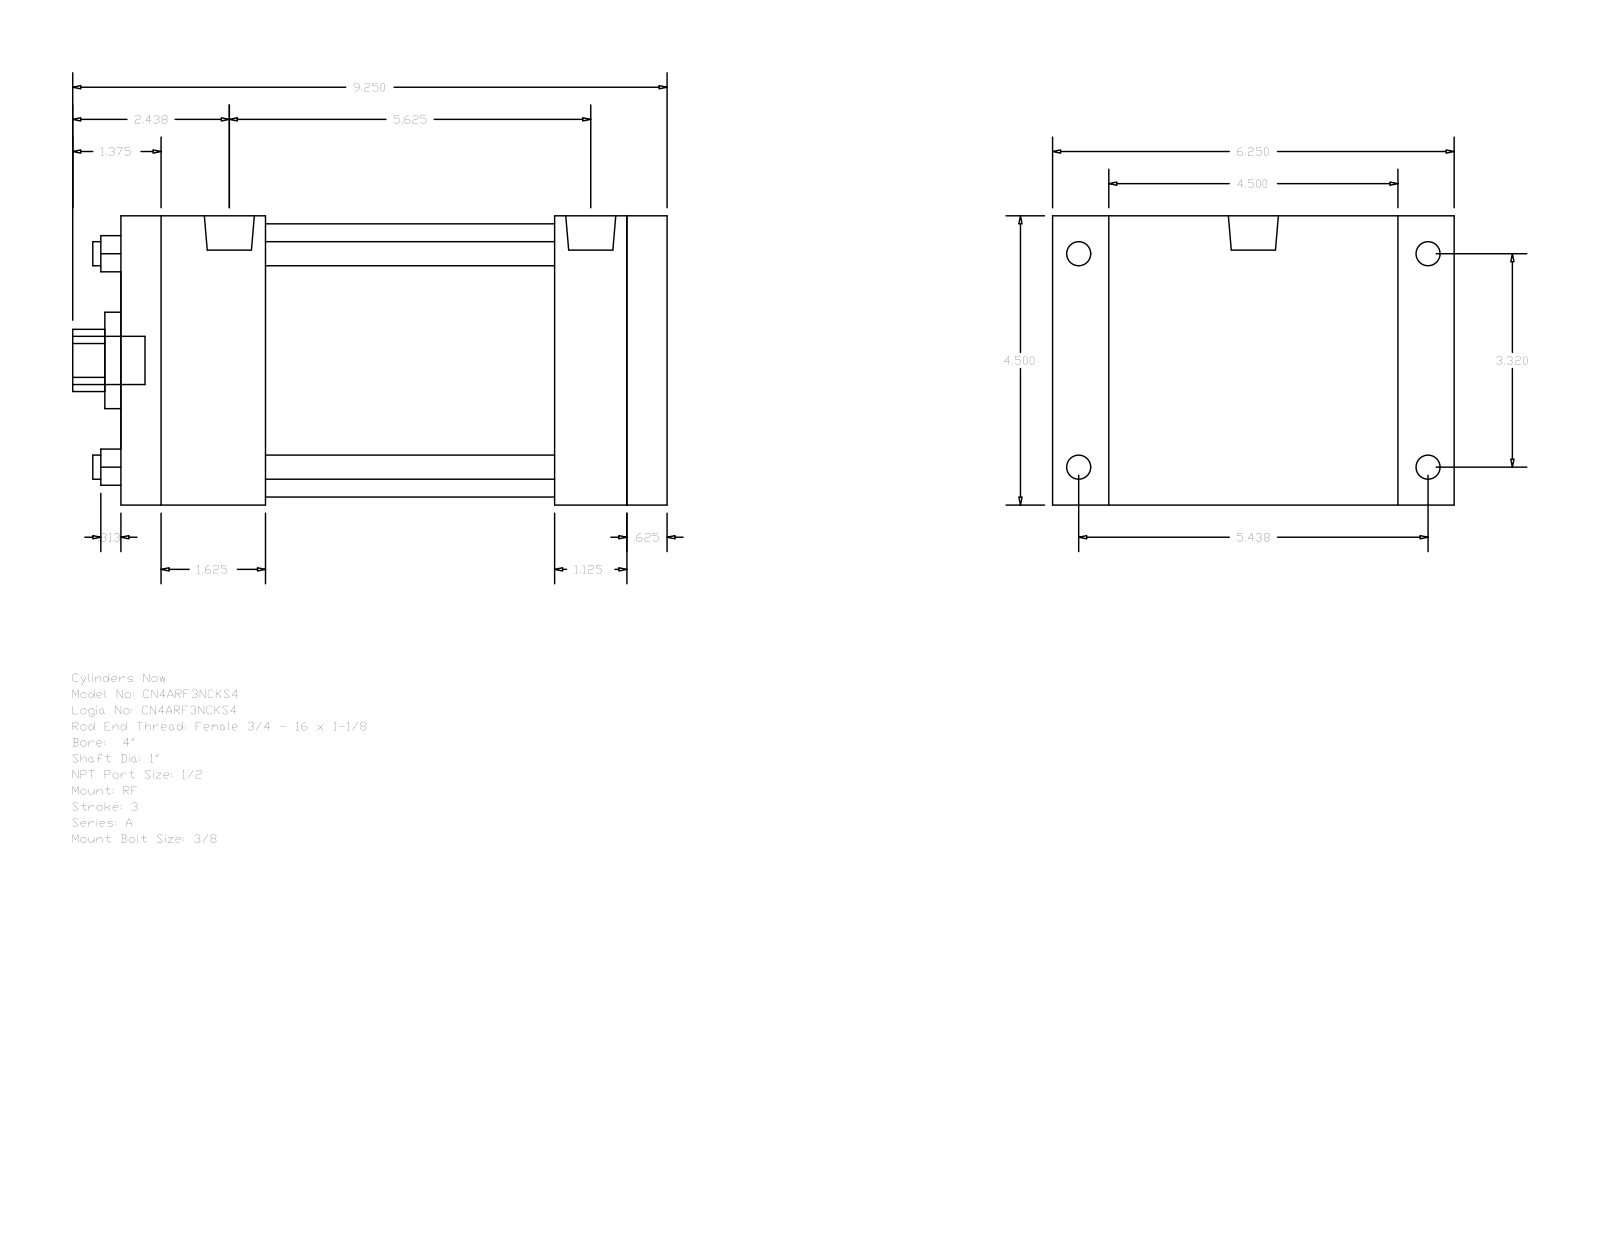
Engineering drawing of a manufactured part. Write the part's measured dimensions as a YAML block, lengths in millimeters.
part_name: "A_RF__0400_1"
step_written_by: "GSSL Pune (CONFIG_CONTROL_DESIGN)"
units: millimeters
bodies: {solids: 0, faces: 92, planar: 64, cylindrical: 28, other: 0}
overall_size: [234.95, 158.75, 114.3]
round_holes:
  - {diameter: 9.53, count: 4}
  - {diameter: 25.4, count: 1}
  - {diameter: 38.1, count: 1}
  - {diameter: 107.95, count: 1}
round_bosses_or_shafts:
  - {diameter: 9.53, count: 4}
  - {diameter: 8.73, count: 4}
  - {diameter: 19.77, count: 2}
  - {diameter: 19.05, count: 1}
partial_cylinders:
  - {radius: 12.29, count: 1}
face_to_face_distances: [114.3, 215.9, 200.02, 15.88, 28.57, 22.23, 136.53, 171.45, 44.45, 57.15]
hole_center_spacings: [59.62, 84.32, 119.25]
